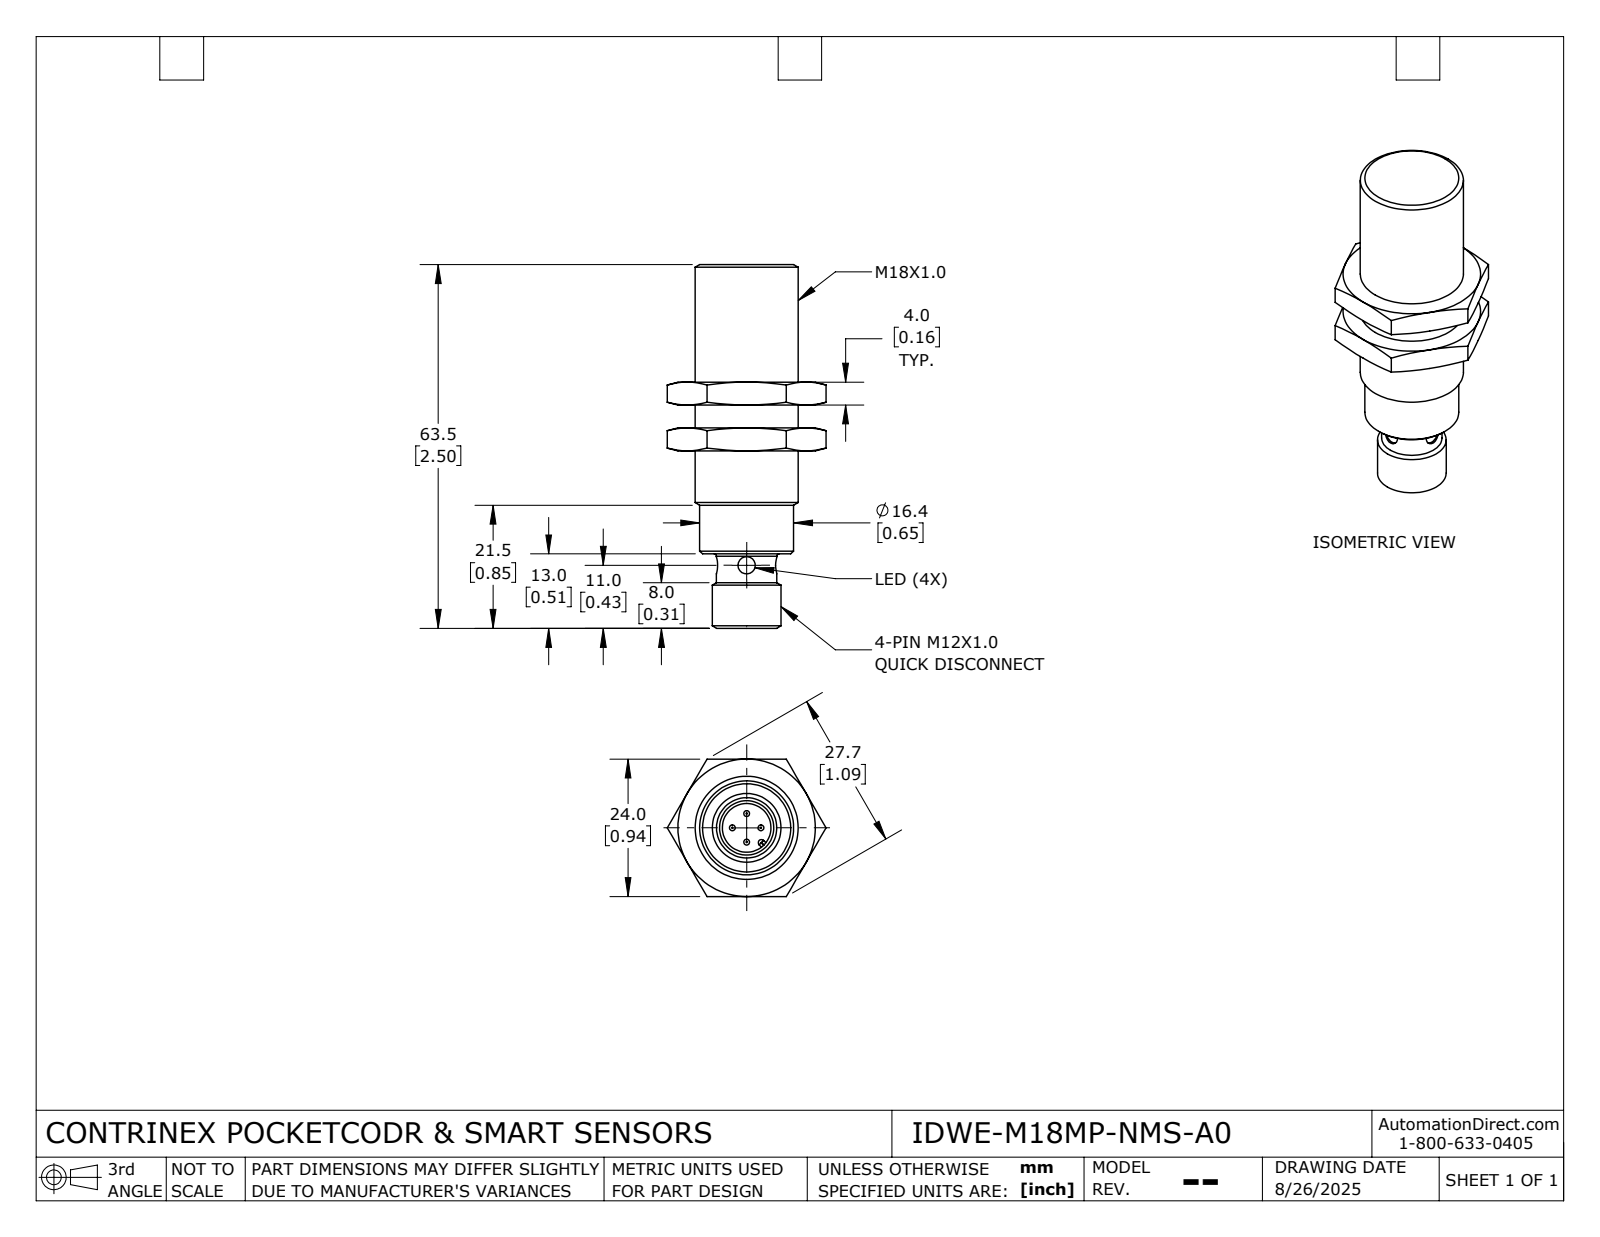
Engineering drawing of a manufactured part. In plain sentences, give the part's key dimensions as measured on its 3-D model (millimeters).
The part is named "IDWE-M18MP-NMS-A0". Its 3-D file was written by "SolidWorks 2024 (AUTOMOTIVE_DESIGN)". It is 3 solids with 89 faces: 31 planar, 18 cylindrical and 40 other. Overall it measures 63.5 by 27.7 by 24 millimeters. Its volume is 15 500 cubic millimeters and its surface area 6 170 square millimeters. Round holes: 2 of diameter 3, 1 of diameter 3, 1 of diameter 8.5, 1 of diameter 16.9. Round bosses or shafts: 4 of diameter 1, 1 of diameter 18, 1 of diameter 16.4, 1 of diameter 12, 1 of diameter 10.5. Partial cylindrical surfaces (rounded edges, fillets, slot ends): 2 of radius 0.5, 1 of radius 0.5. The main face-to-face distances are 4, 8, 24, 12, 24.5, 32.5, 20.5, 28.5, 30, 50.5.
